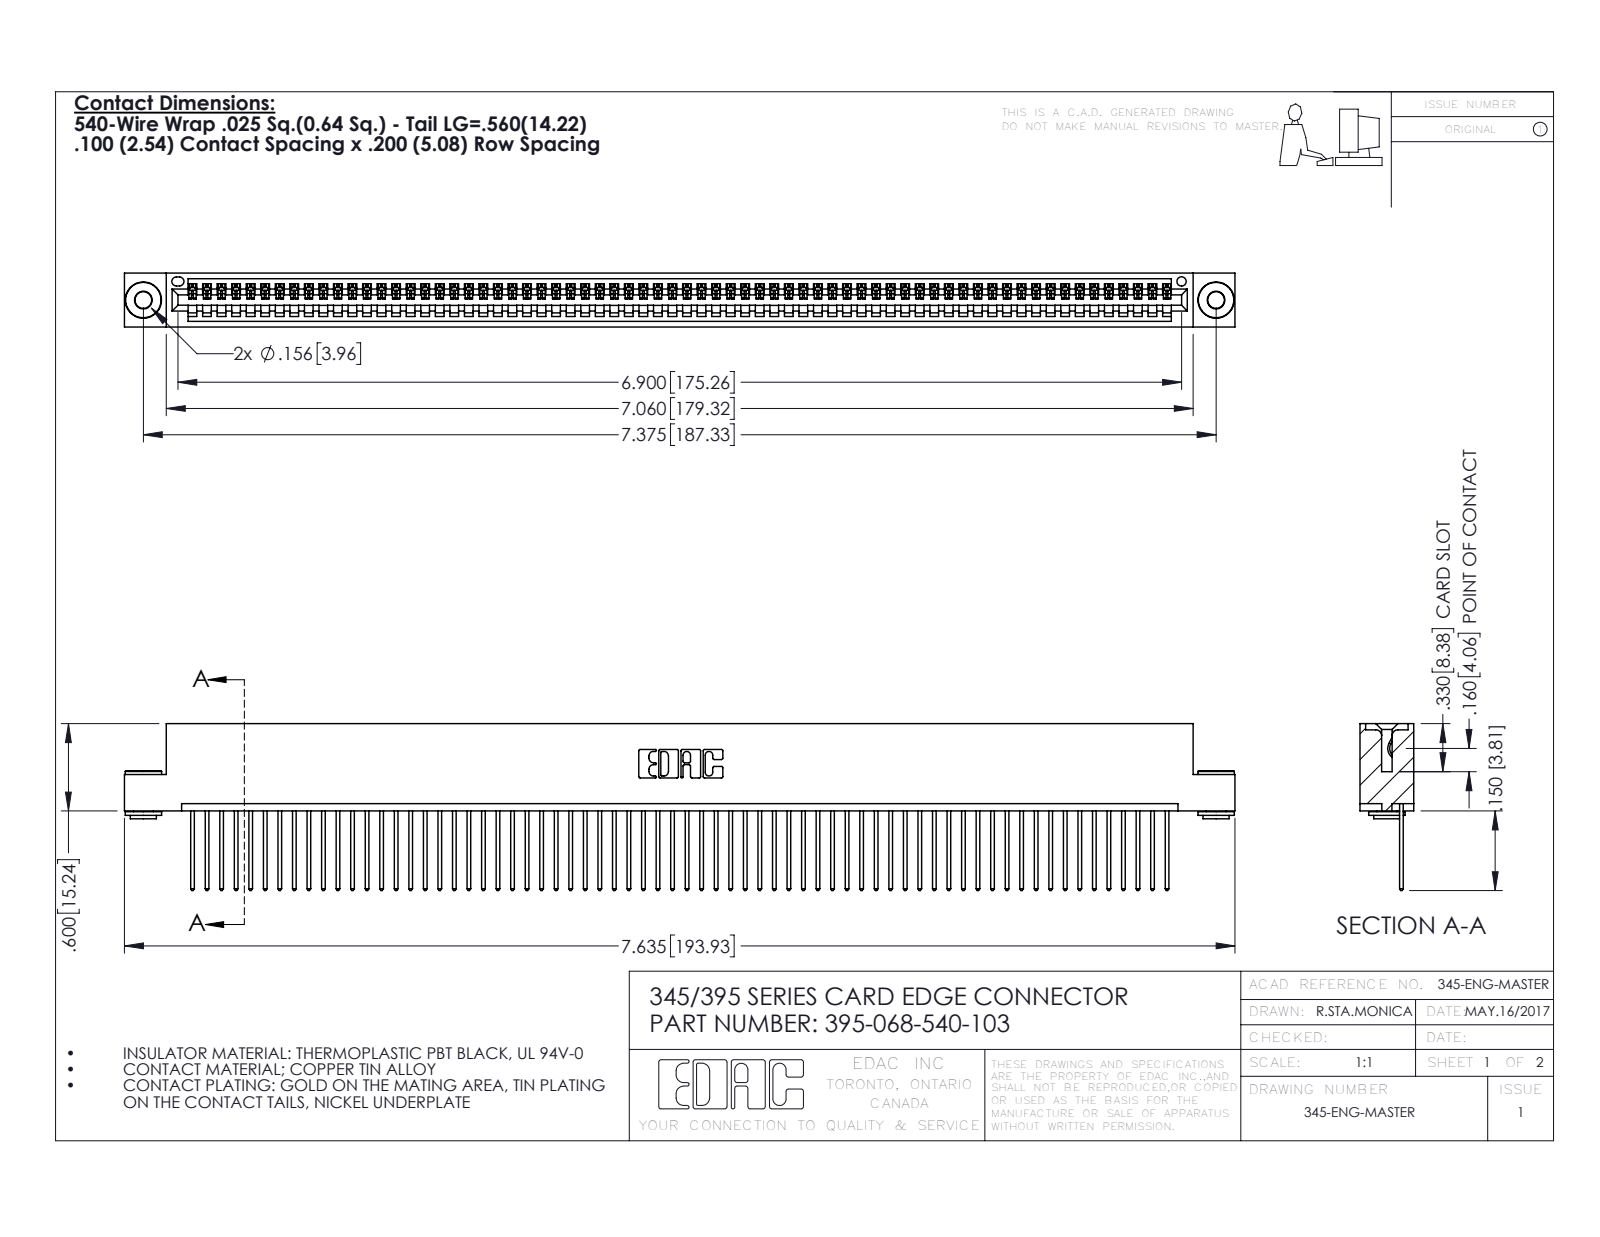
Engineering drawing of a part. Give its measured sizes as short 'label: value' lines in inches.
name: 345-292-001_345-293-140; 345-250-002_345-250-002-102; 345 Part_Flush Mounting Lugs - 0.156 Dia-TH; 395-068-540-103
written by: SolidWorks 2016 (CONFIG_CONTROL_DESIGN)
unit: in
bodies: 71 solids, 4108 faces (2810 planar, 1290 cylindrical, 8 other)
size: 7.635 × 1.147 × 0.37
volume: 1.144 in³; area: 40.52 in²
holes: 2× ⌀0.116, 2× ⌀0.156, 1× ⌀0.064
bosses: 2× ⌀0.25, 2× ⌀0.18, 2× ⌀0.136
rounds: 136× R0.006, 136× R0.01, 22× R0.01, 6× R0.007, 6× R0.031, 3× R0.026, 2× R0.031, 2× R0.04
face distances: 0.072, 0.298, 0.025, 0.37, 0.098, 0.272, 0.2, 0.225, 0.149, 0.072
hole spacings: 0.27, 7.139, 7.375
